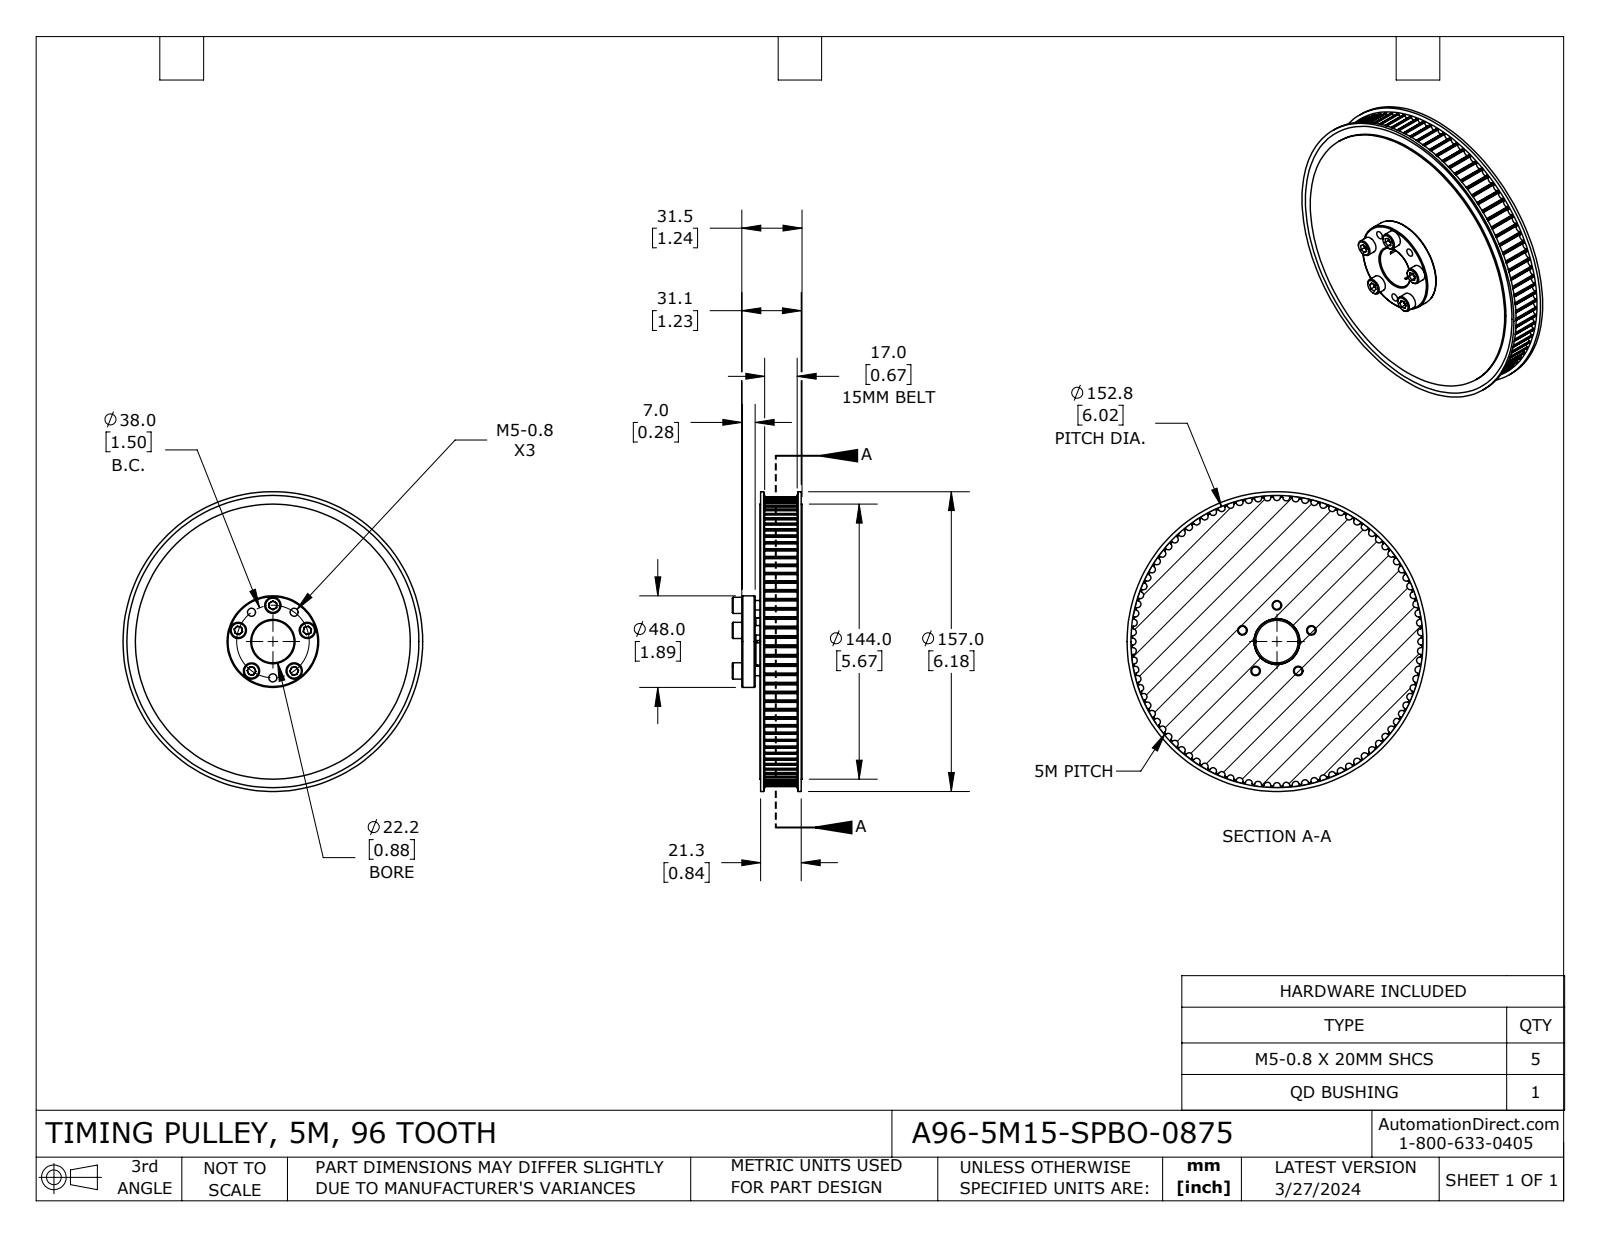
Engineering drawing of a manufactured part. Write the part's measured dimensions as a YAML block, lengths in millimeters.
part_name: "A96-5M15-SPBO-0875"
step_written_by: "SolidWorks 2021 (CONFIG_CONTROL_DESIGN)"
units: millimeters
bodies: {solids: 9, faces: 714, planar: 101, cylindrical: 547, other: 66}
overall_size: [157, 157, 36.5]
volume: 390980
surface_area: 76236
round_holes:
  - {diameter: 4.2, count: 8}
  - {diameter: 5.5, count: 5}
  - {diameter: 22.22, count: 1}
  - {diameter: 24.83, count: 1}
  - {diameter: 144, count: 1}
round_bosses_or_shafts:
  - {diameter: 8.5, count: 5}
  - {diameter: 5, count: 5}
  - {diameter: 157, count: 1}
  - {diameter: 48, count: 1}
  - {diameter: 24.82, count: 1}
partial_cylinders:
  - {radius: 0.3, count: 192}
  - {radius: 1.82, count: 96}
  - {radius: 75.83, count: 1}
face_to_face_distances: [22, 2.5, 19.5, 0.9, 21.1, 1.6, 18.6, 17, 20.2, 12]
hole_center_spacings: [19, 36.14, 30.74, 11.75, 22.34, 38, 11.74, 22.33]
